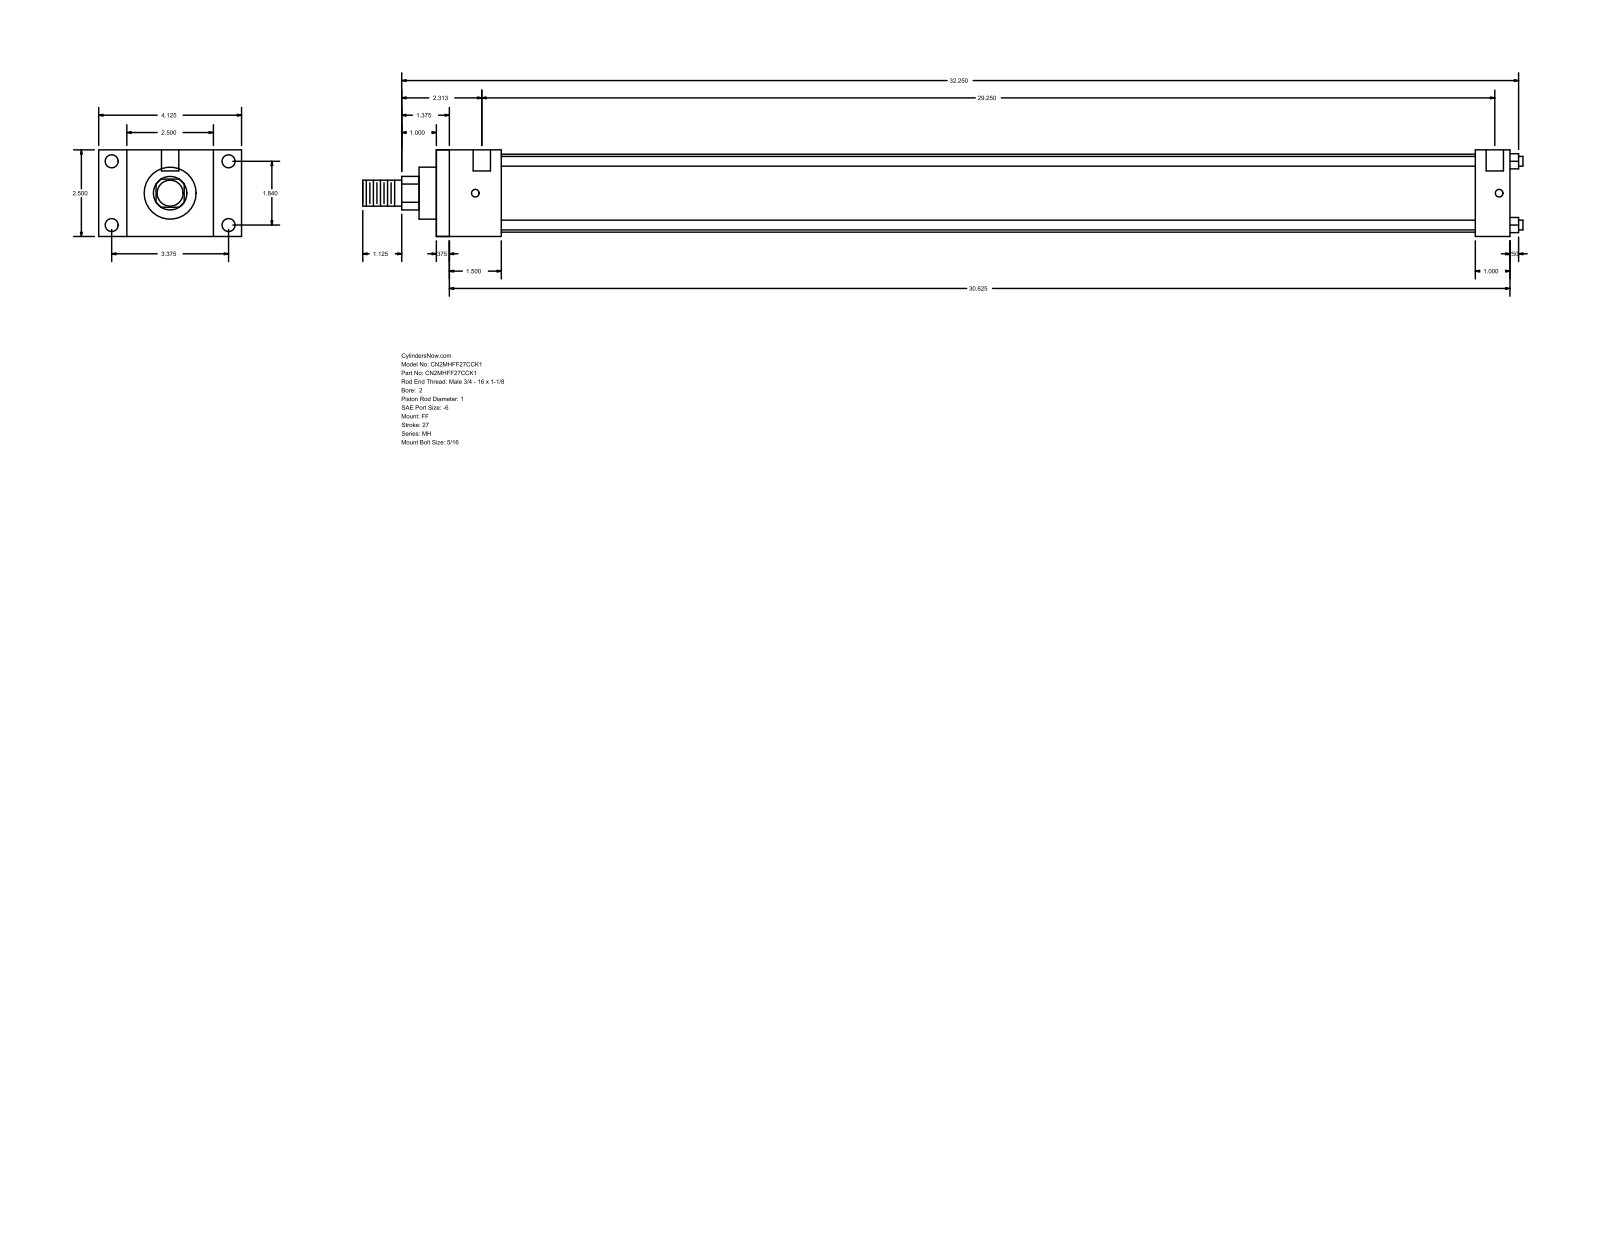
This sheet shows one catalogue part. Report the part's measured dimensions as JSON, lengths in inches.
{"part_name": "MH_FF__0200_1", "step_written_by": "GSSL Pune (CONFIG_CONTROL_DESIGN)", "units": "inches", "bodies": {"solids": 0, "faces": 92, "planar": 64, "cylindrical": 28, "other": 0}, "overall_size": [33.5, 4.125, 2.5], "round_holes": [[0.219, 4], [0.375, 4], [0.5, 2]], "round_bosses_or_shafts": [[0.281, 4], [2.25, 1], [1.5, 1], [1, 1], [0.75, 1]], "partial_cylinders_radius": [[0.484, 1]], "face_to_face_distances": [2.5, 31, 0.375, 30.625, 0.813, 1, 1.875, 30, 1.5, 29.625], "hole_center_spacings": [1.84, 3.375, 3.844, 29.562, 0.125, 0.187, 29.25, 29.375]}
